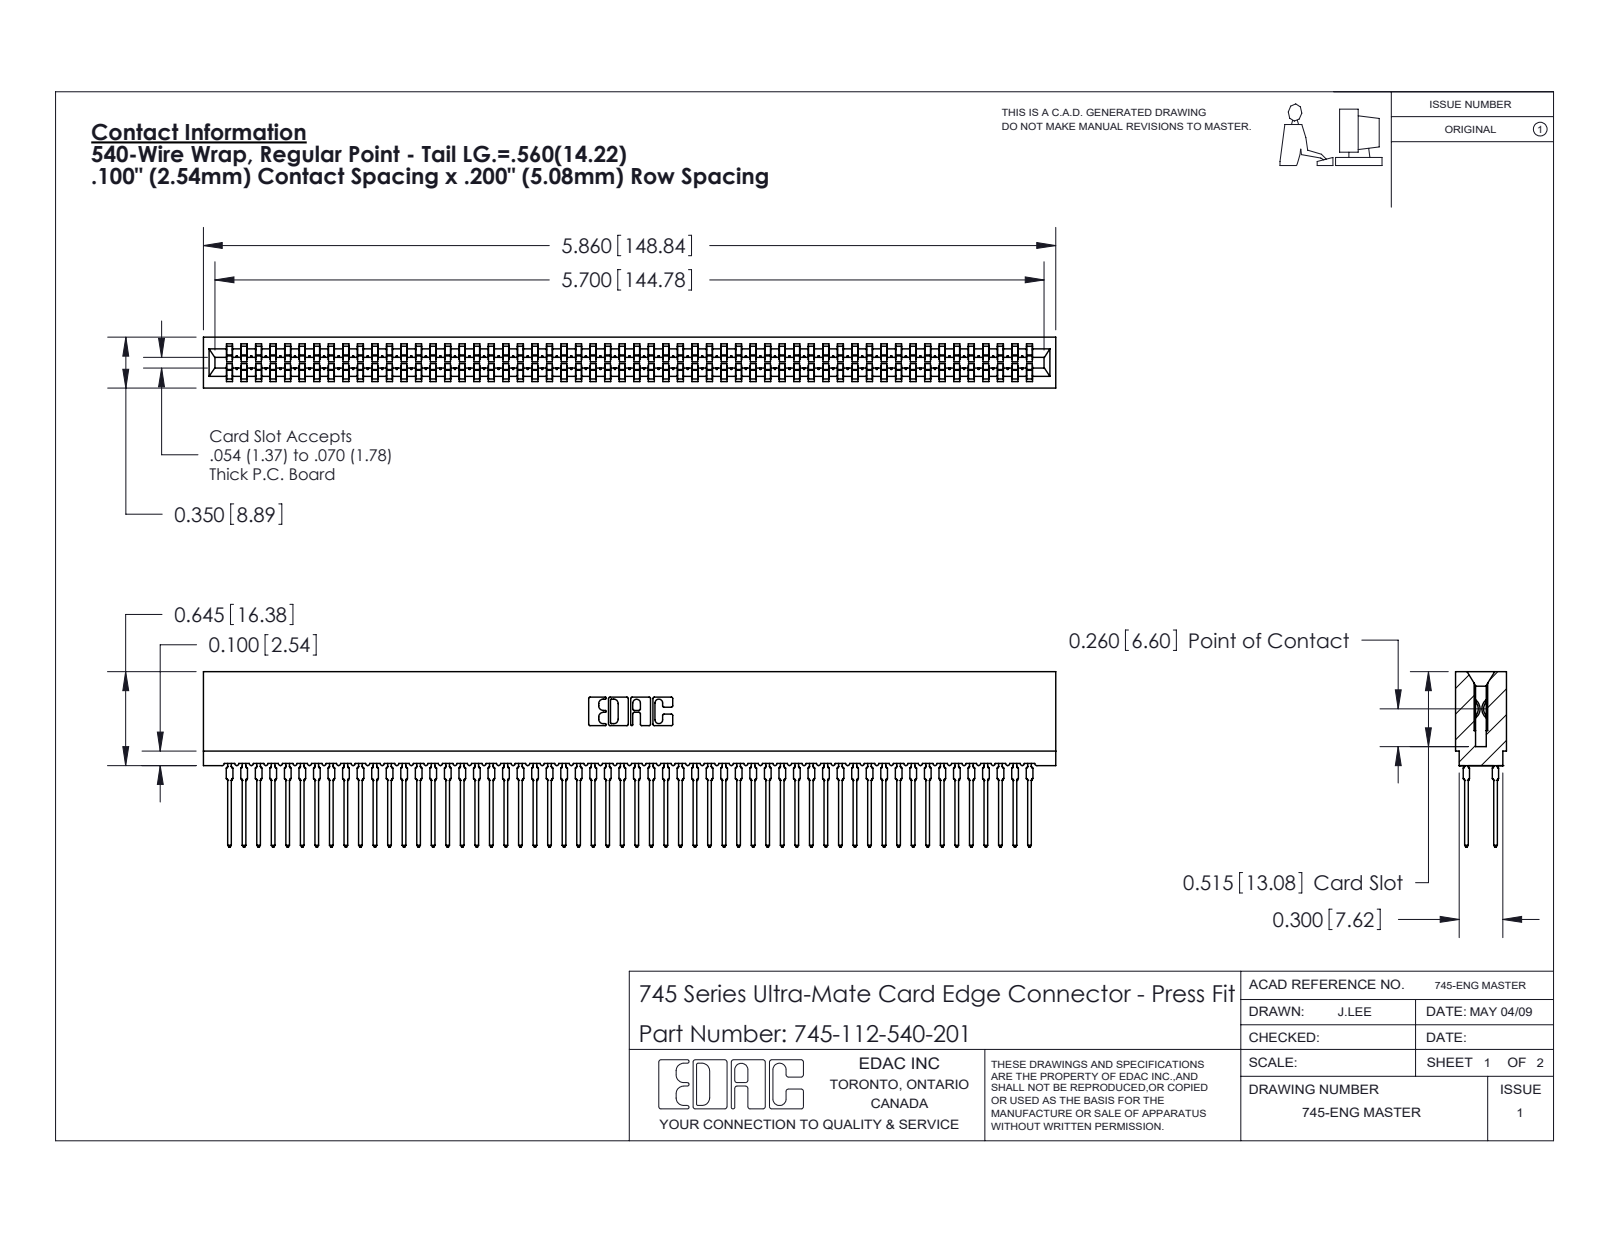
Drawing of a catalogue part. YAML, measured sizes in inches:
part_name: "745-112-540-201; 745-292-001_540; 745 Part_Insulator Option - 01"
step_written_by: "SolidWorks 2020 (CONFIG_CONTROL_DESIGN)"
units: inches
bodies: {solids: 113, faces: 10119, planar: 5207, cylindrical: 2000, other: 2912}
overall_size: [5.86, 1.206, 0.35]
volume: 0.833
surface_area: 45.52
partial_cylinders:
  - {radius: 0.021, count: 224}
  - {radius: 0.015, count: 112}
  - {radius: 0.01, count: 22}
  - {radius: 0.005, count: 8}
  - {radius: 0.011, count: 8}
  - {radius: 0.007, count: 6}
  - {radius: 0.031, count: 6}
  - {radius: 0.026, count: 3}
face_to_face_distances: [0.063, 0.287, 0.35, 0.2, 0.045, 0.305, 0.018, 0.243, 0.138, 0.212]
